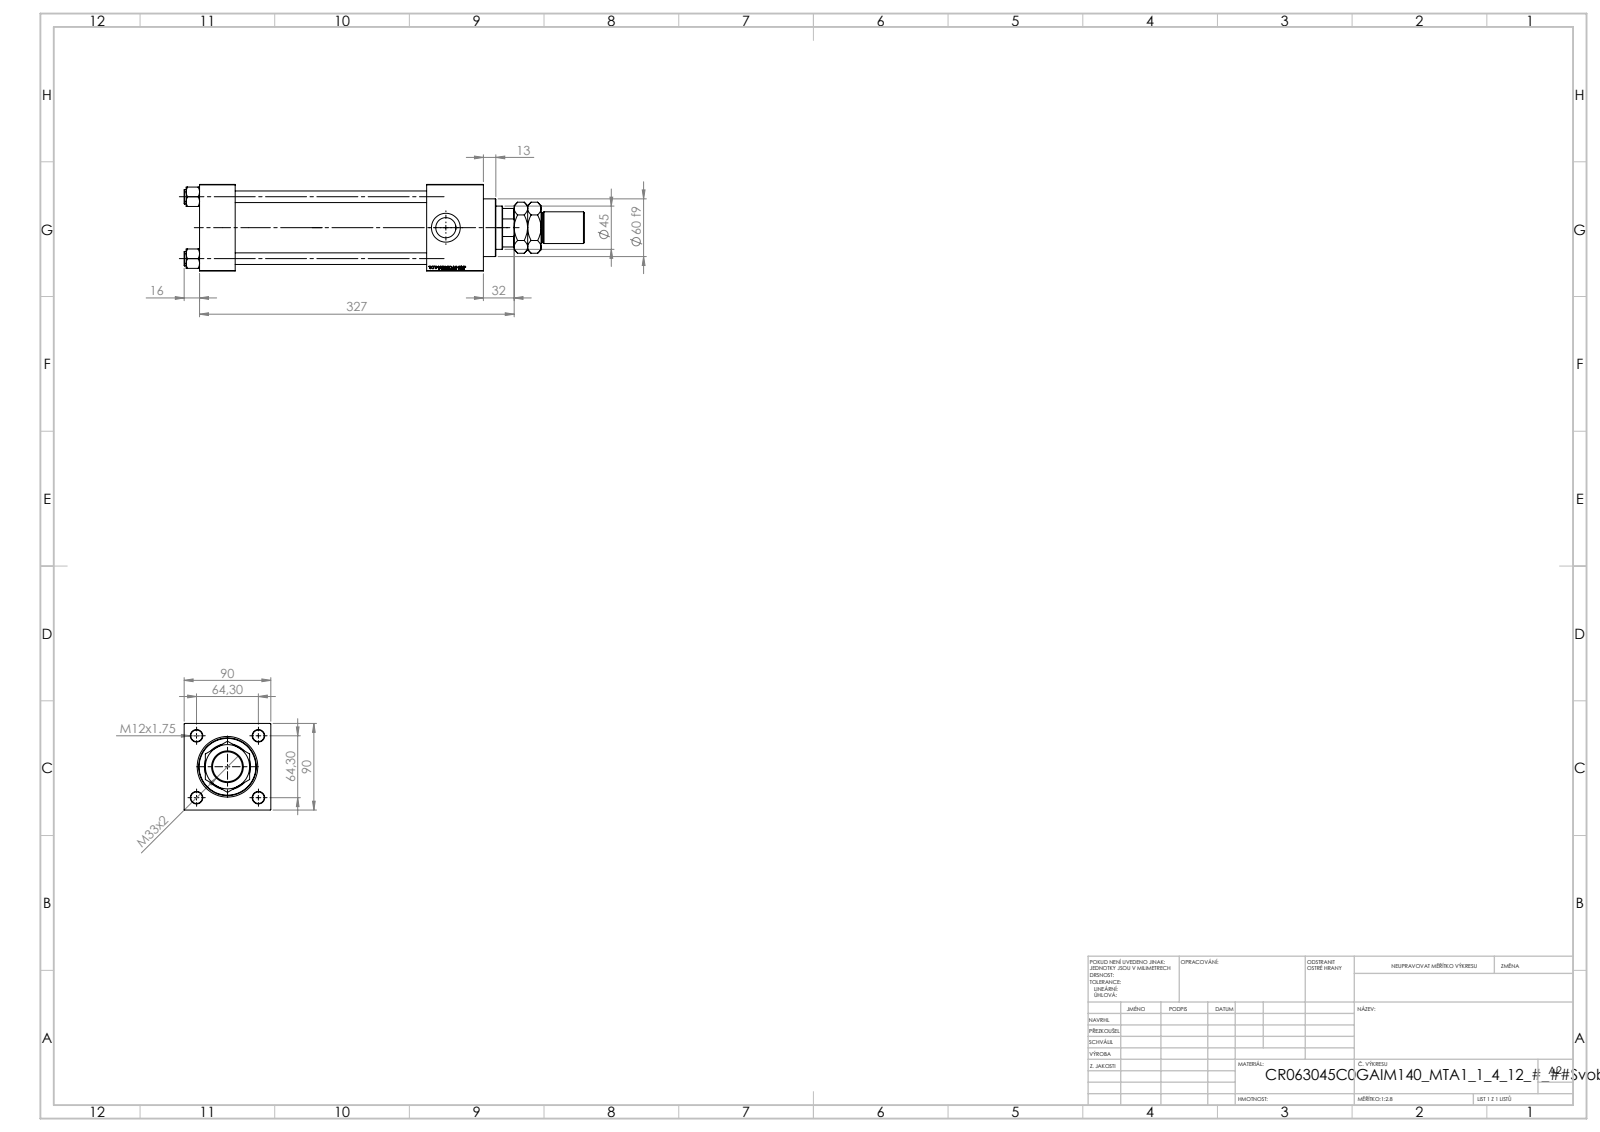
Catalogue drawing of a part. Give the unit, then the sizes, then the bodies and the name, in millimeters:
Units: millimetres
Overall size (bounding box): 416 × 90 × 90
Round holes (diameter × count): ⌀12 ×4, ⌀7 ×2, ⌀20.96 ×2, ⌀30 ×2, ⌀31.5 ×1, ⌀45 ×1, ⌀48 ×1, ⌀50 ×1, ⌀60 ×1, ⌀63 ×1
Round bosses / shafts (diameter × count): ⌀15 ×4, ⌀69 ×1, ⌀33 ×1, ⌀31 ×1
Partial cylindrical surfaces — rounded edges, fillets, slot ends (radius × count): R22 ×1
Main face-to-face distances: 90, 37, 59, 236, 199, 295, 258, 46, 32, 290
Hole centre spacings: 45.47, 64.3, 90.93
Volume: 1 460 000 mm³ · Surface area: 301 557 mm²
Bodies: 12 solids, 1195 faces (540 planar, 89 cylindrical, 566 other)
Part name (STEP PRODUCT): MTA; V215_VC_A; V215CR_VCP_C; V215CR_C_Body (+2 more)
STEP written by: SolidWorks 2019 (CONFIG_CONTROL_DESIGN)
